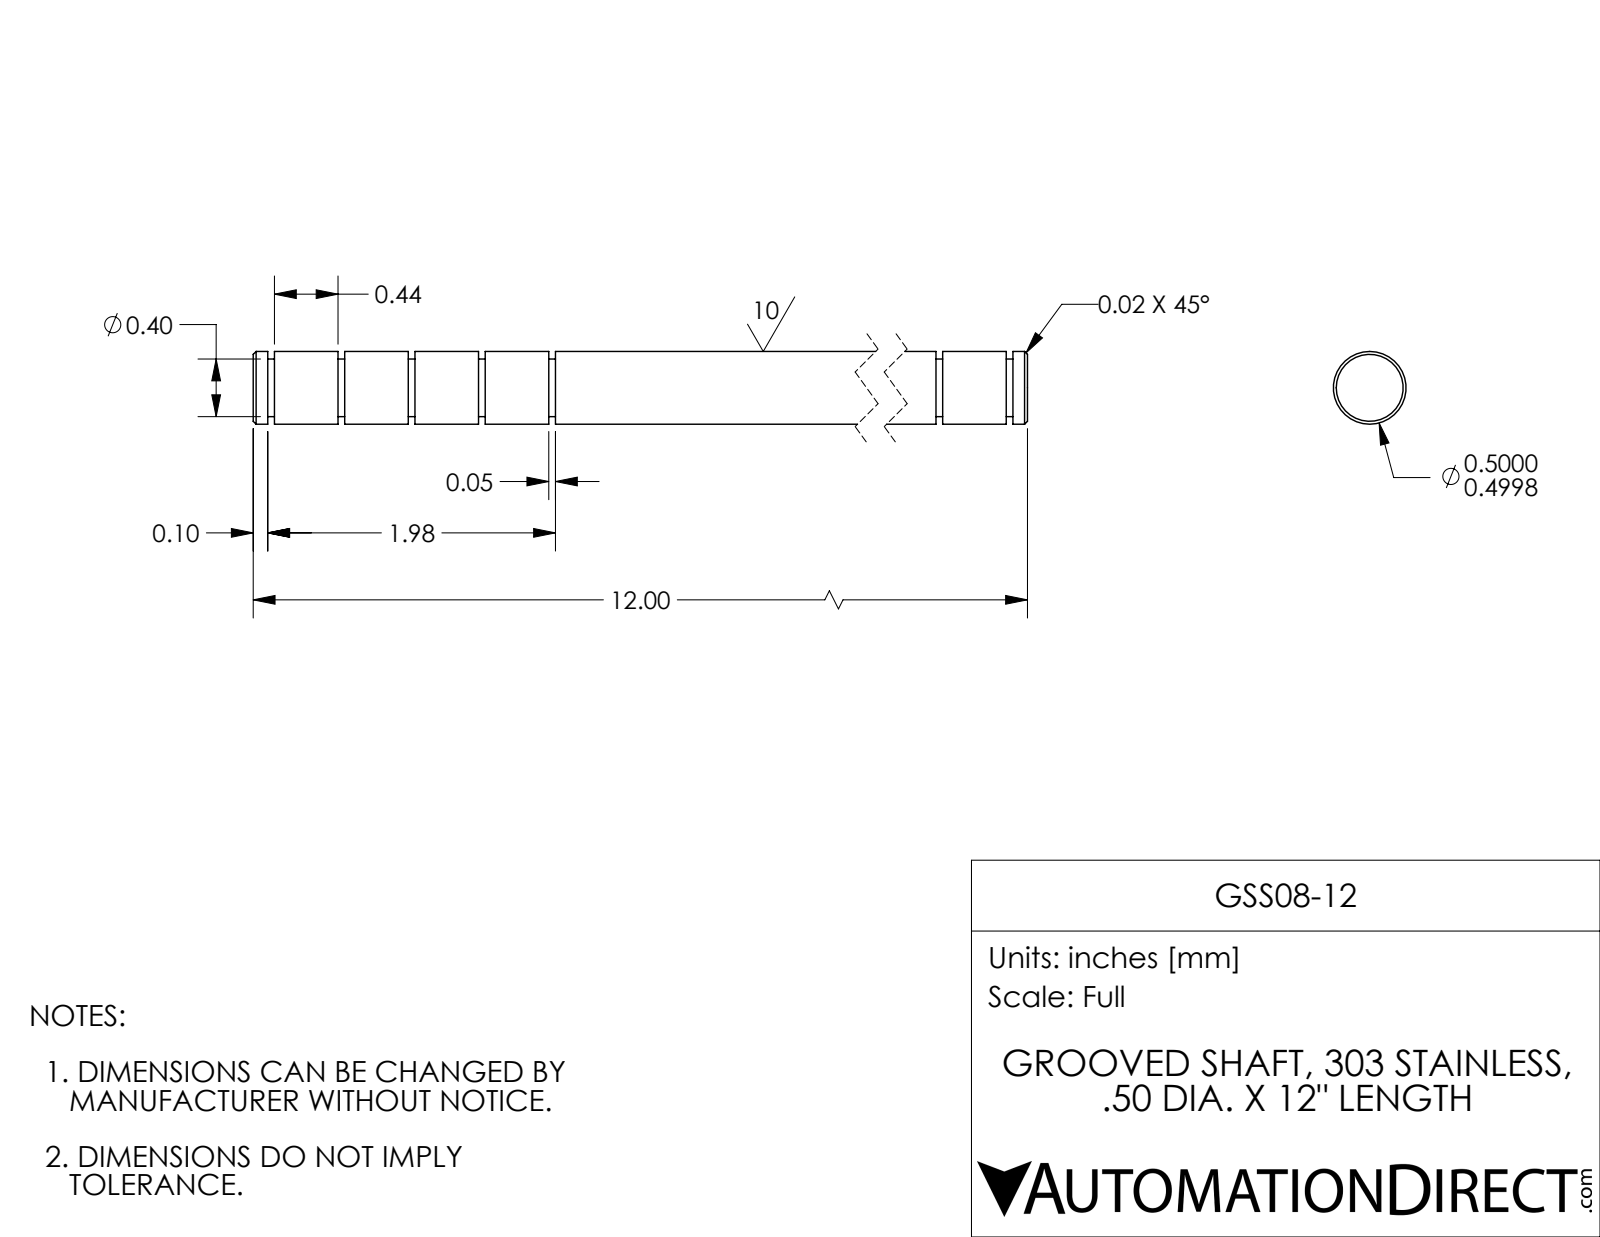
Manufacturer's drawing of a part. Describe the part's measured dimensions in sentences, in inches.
The part is named "GSS08-12". Its 3-D file was written by "SolidWorks 2017 (AUTOMOTIVE_DESIGN)". It is 1 solid with 50 faces: 16 planar, 30 cylindrical and 4 other. Overall it measures 12 by 0.5 by 0.5 inches. Its volume is 2.332 cubic inches and its surface area 20.12 square inches. Round bosses or shafts: 1 of diameter 0.5, 1 of diameter 0.396. The main face-to-face distances are 0.483, 0.046, 0.437, 1.449, 11.271, 9.822, 0.966, 0.529, 1.012, 10.788.
